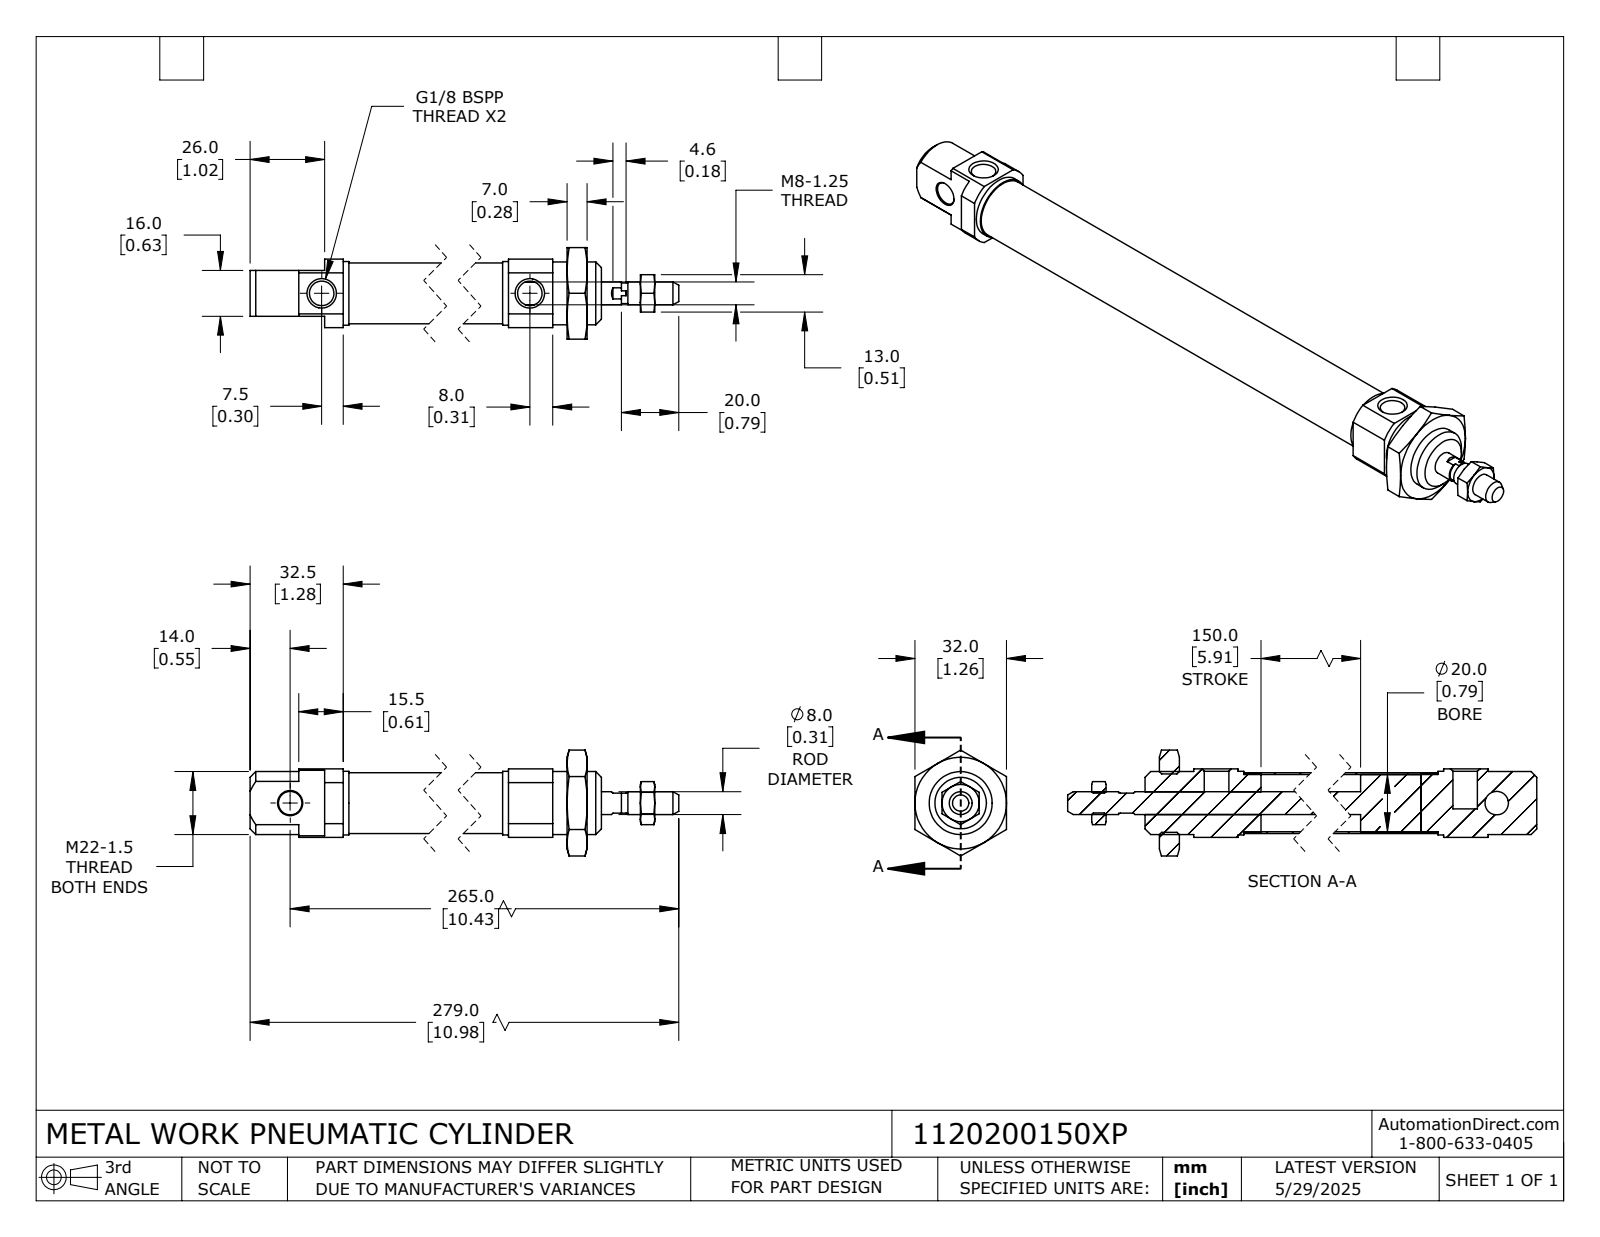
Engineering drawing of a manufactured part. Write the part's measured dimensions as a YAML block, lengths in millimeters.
part_name: "1120200150XP; 1120200150XP_BODY; 1120200150XP_ROD"
step_written_by: "SolidWorks 2024 (CONFIG_CONTROL_DESIGN)"
units: millimeters
bodies: {solids: 6, faces: 147, planar: 56, cylindrical: 45, other: 46}
overall_size: [279, 36.95, 32]
volume: 57420
surface_area: 43580
round_holes:
  - {diameter: 8.57, count: 2}
  - {diameter: 6.92, count: 1}
  - {diameter: 8.2, count: 1}
  - {diameter: 20, count: 1}
  - {diameter: 20.38, count: 1}
round_bosses_or_shafts:
  - {diameter: 22.2, count: 1}
  - {diameter: 22, count: 1}
  - {diameter: 21.27, count: 1}
  - {diameter: 20.15, count: 1}
  - {diameter: 8, count: 1}
  - {diameter: 7.2, count: 1}
partial_cylinders:
  - {radius: 13.95, count: 1}
face_to_face_distances: [3.97, 19.97, 23.94, 8, 40.5, 211.5, 7, 5, 206.5, 199.5]
hole_center_spacings: [202]
